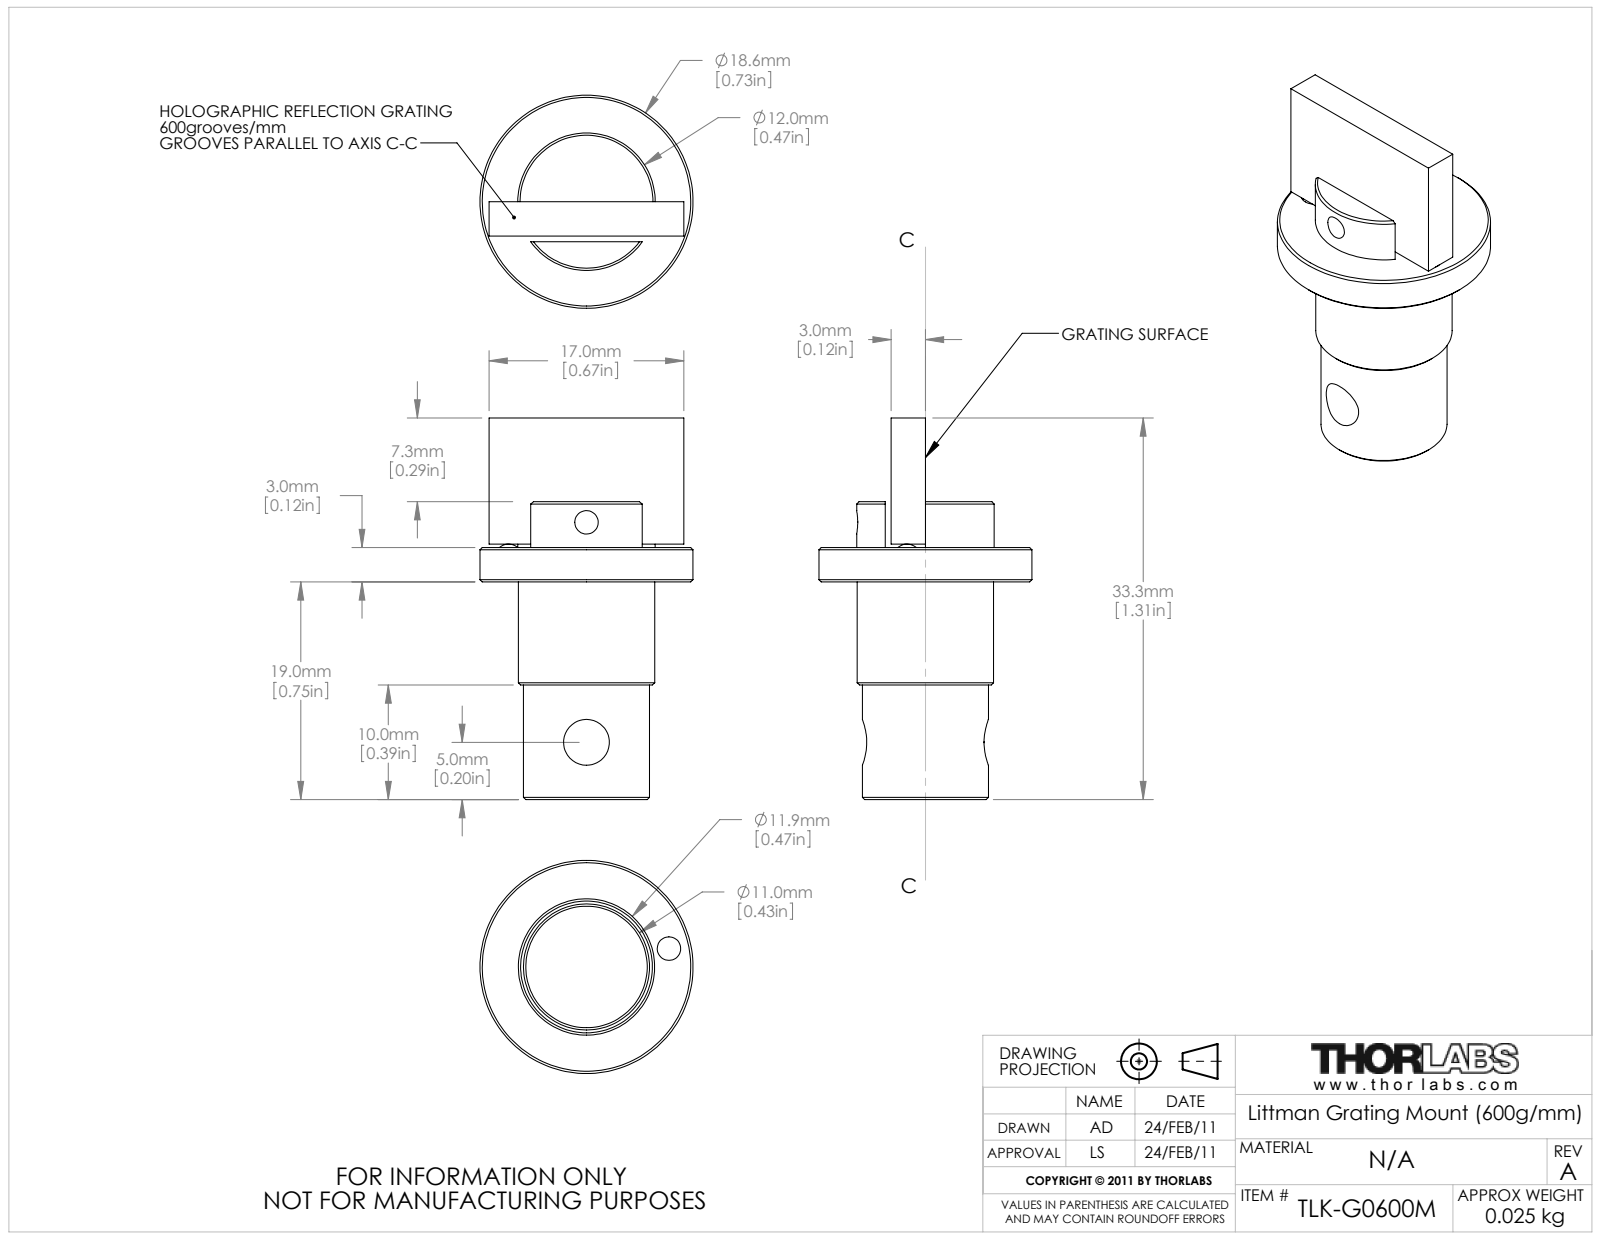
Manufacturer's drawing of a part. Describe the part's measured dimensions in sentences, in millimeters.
The part is named "21568-E0W". Its 3-D file was written by "SolidWorks 2009 (AUTOMOTIVE_DESIGN)". It is 3 solids with 45 faces: 15 planar, 17 cylindrical and 13 other. Overall it measures 33.3 by 18.6 by 18.6 millimeters. Its volume is 3 461 cubic millimeters and its surface area 2 291 square millimeters. Round holes: 2 of diameter 2.05, 1 of diameter 2.6, 1 of diameter 4. Round bosses or shafts: 1 of diameter 18.6, 1 of diameter 12, 1 of diameter 11.9, 1 of diameter 11. The main face-to-face distances are 3, 19, 22, 26, 7, 4, 22.3, 33.3, 3.3, 14.3. The hole center spacings are 14, 19.2.
